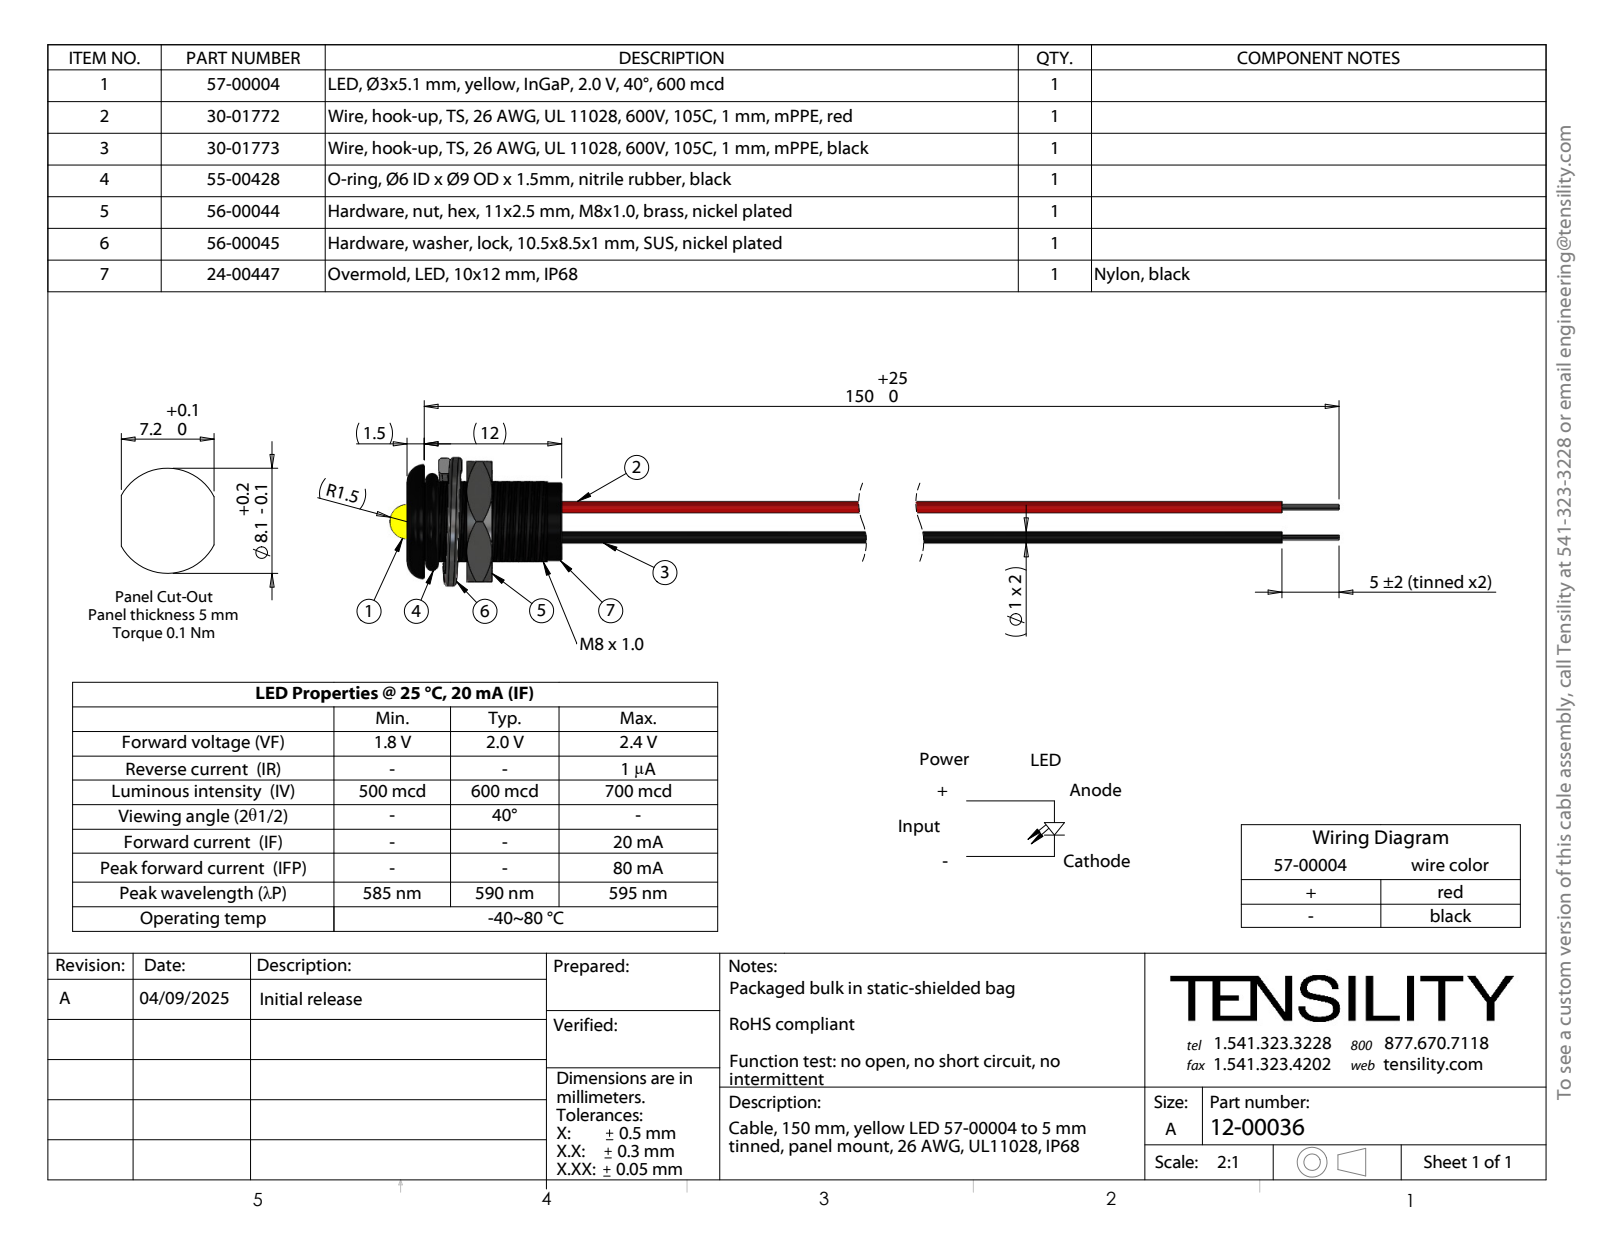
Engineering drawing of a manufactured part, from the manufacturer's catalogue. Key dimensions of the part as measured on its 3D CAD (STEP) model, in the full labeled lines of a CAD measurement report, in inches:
Part name (STEP PRODUCT): 55-00428; 56-00045_Split washer; 30-01773_stripped and tinned; 56-00044 (+4 more)
STEP written by: SolidWorks 2021 (CONFIG_CONTROL_DESIGN)
Units: inches
Bodies: 57 solids, 555 faces (186 planar, 246 cylindrical, 123 other)
Overall size (bounding box): 6.693 × 0.477 × 0.441
Volume: 0.061 in³ · Surface area: 9.157 in²
Round holes (diameter × count): ⌀0.039 ×2
Round bosses / shafts (diameter × count): ⌀0.039 ×2, ⌀0.02 ×2, ⌀0.268 ×1, ⌀0.118 ×1
Partial cylindrical surfaces — rounded edges, fillets, slot ends (radius × count): R0.137 ×1, R0.157 ×1
Main face-to-face distances: 0.059, 0.531, 0.472, 0.413, 0.205, 0.146, 0.326, 0.292, 0.233, 0.087
Hole centre spacings: 0.014, 0.015, 0.013, 0.098, 0.099, 0.096, 0.096, 0.101
